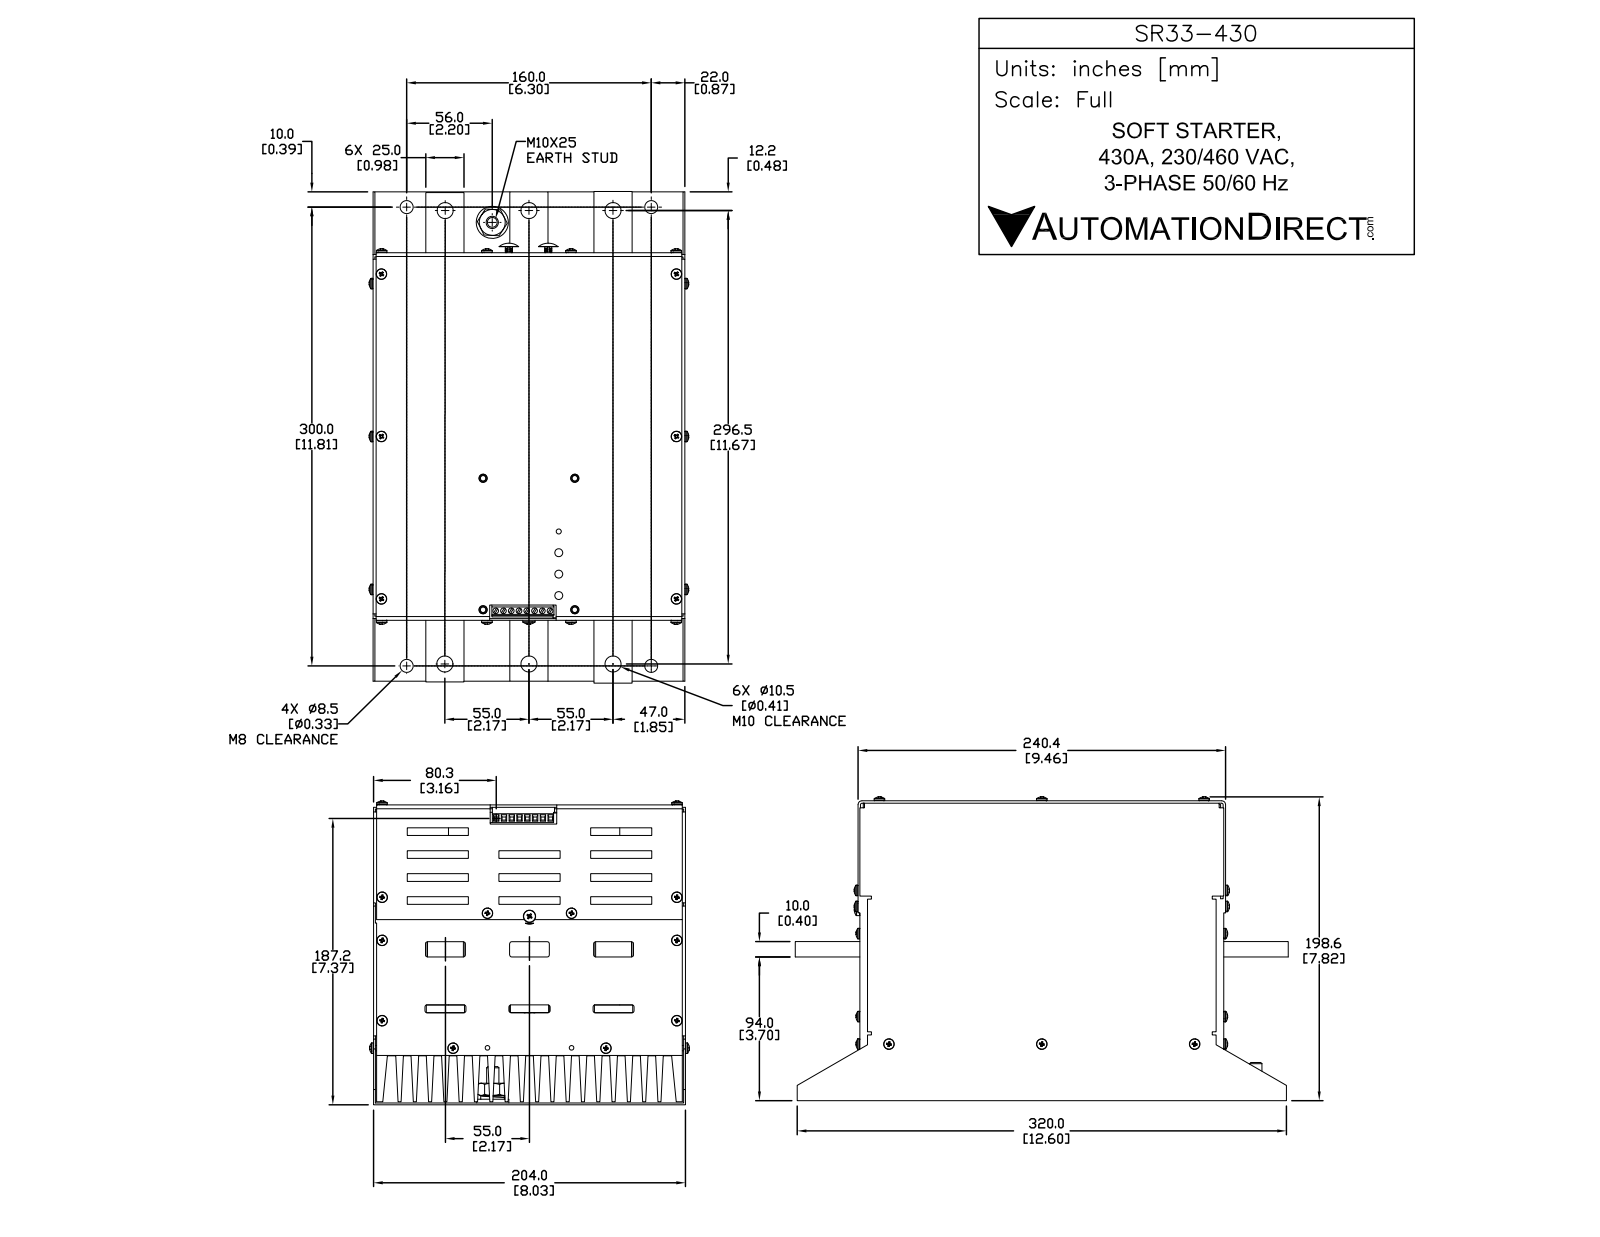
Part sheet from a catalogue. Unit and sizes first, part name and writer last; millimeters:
Units: millimetres
Overall size (bounding box): 322.8 × 203 × 199.1
Round holes (diameter × count): ⌀3.82 ×8, ⌀8.5 ×4
Round bosses / shafts (diameter × count): ⌀6.9 ×14, ⌀16 ×7, ⌀8 ×7
Partial cylindrical surfaces — rounded edges, fillets, slot ends (radius × count): R2 ×14, R1 ×8
Main face-to-face distances: 9.99, 19.98, 29.97, 39.96, 49.95, 59.94, 15, 69.93, 79.92, 89.91
Hole centre spacings: 4.92, 9.84, 14.76, 19.68, 24.6, 29.52, 160, 300
Volume: 7 932 000 mm³ · Surface area: 999 241 mm²
Bodies: 2 solids, 1114 faces (755 planar, 153 cylindrical, 206 other)
Part name (STEP PRODUCT): SR33-430
STEP written by: SolidWorks 2013 (AUTOMOTIVE_DESIGN)
